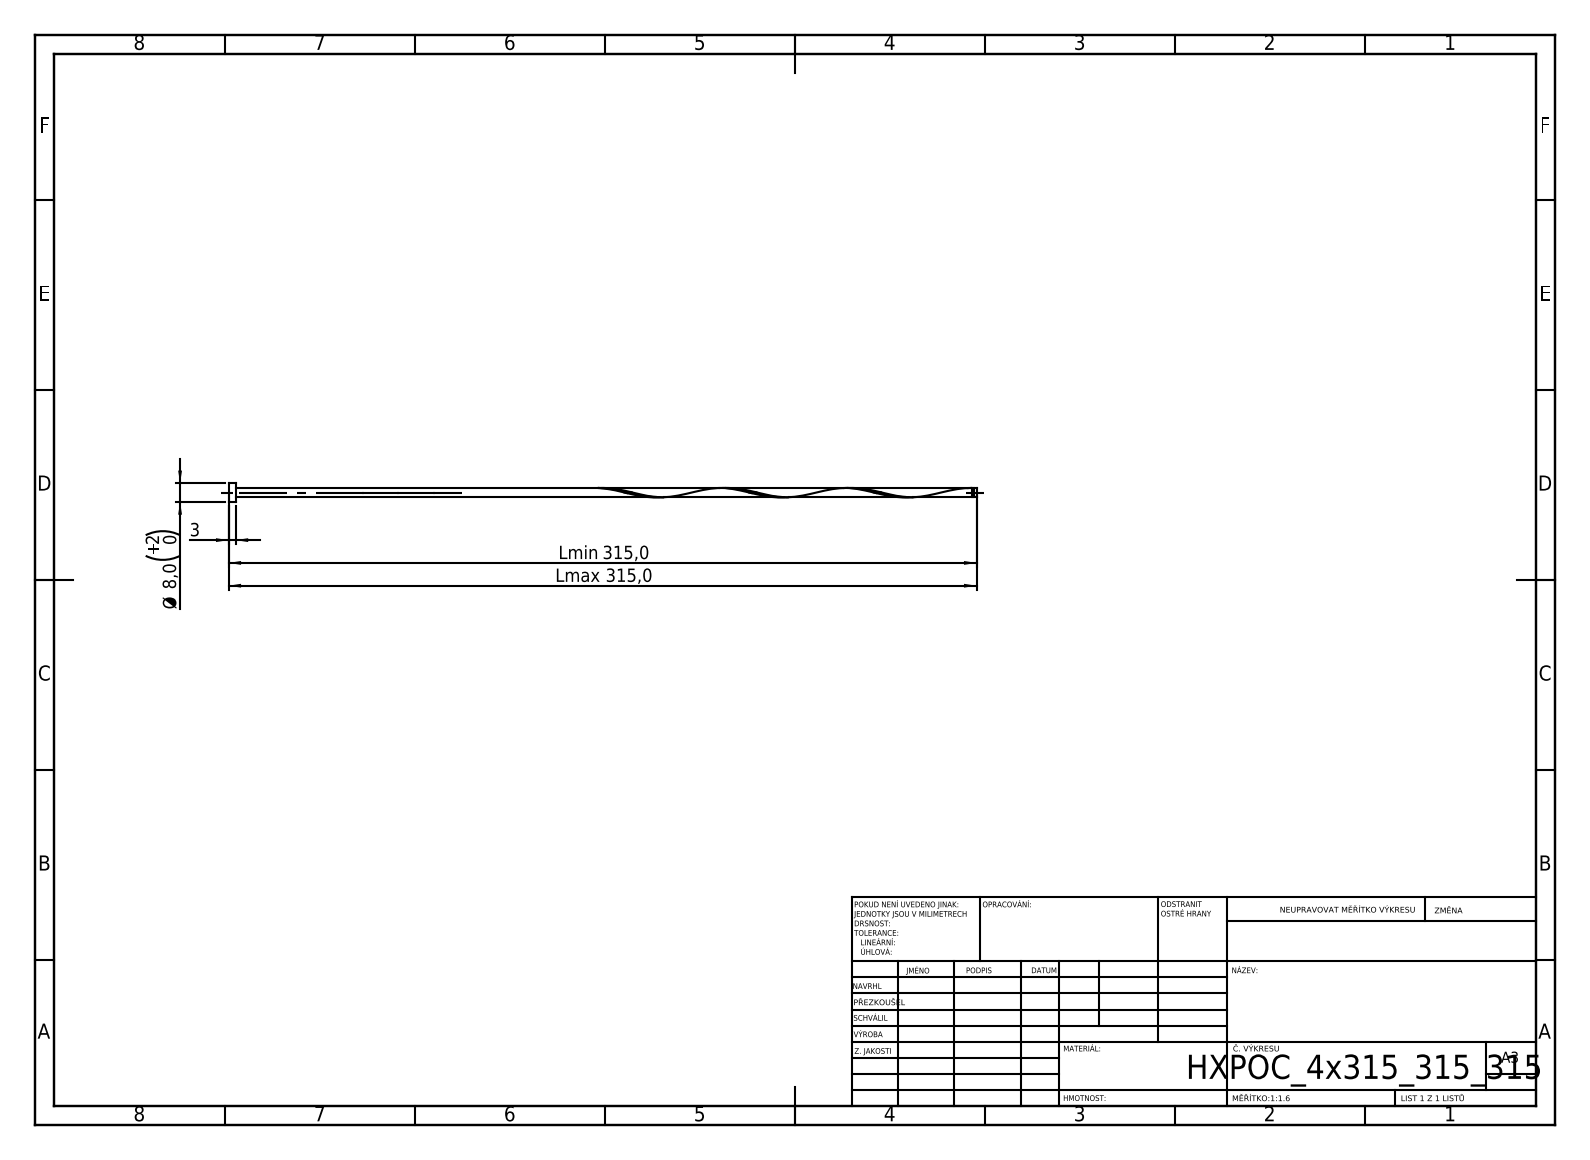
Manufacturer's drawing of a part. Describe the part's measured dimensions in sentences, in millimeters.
Its 3-D file was written by "SolidWorks 2019 (CONFIG_CONTROL_DESIGN)". It is 1 solid with 16 faces: 6 planar, 9 cylindrical and 1 other. Overall it measures 315 by 8 by 8 millimeters. Its volume is 4 910 cubic millimeters and its surface area 5 485 square millimeters. Round bosses or shafts: 1 of diameter 8, 1 of diameter 4, 1 of diameter 3.2. The main face-to-face distances are 3, 315, 312, 313.82, 310.82, 1.18, 313.02, 310.02, 0.8, 1.98.
